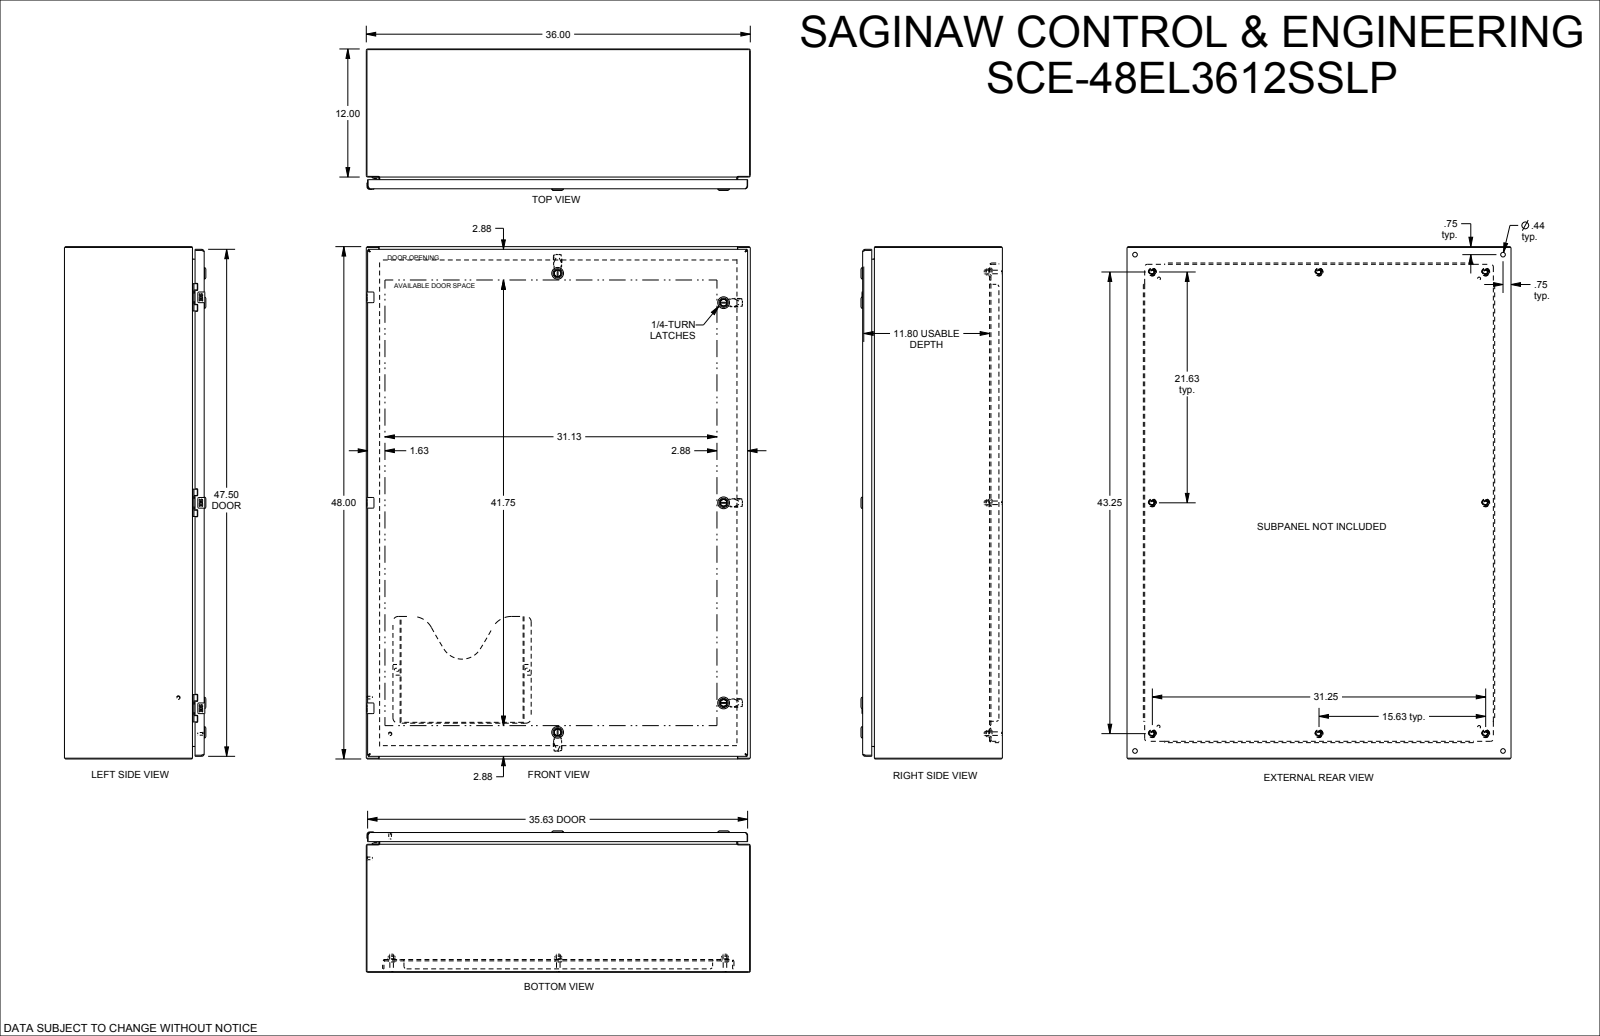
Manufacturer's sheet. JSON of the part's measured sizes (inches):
{"part_name": "SCE-48EL3612SSLP", "step_written_by": "SolidWorks 2019 (CONFIG_CONTROL_DESIGN)", "units": "inches", "bodies": {"solids": 0, "faces": 4985, "planar": 2437, "cylindrical": 1389, "other": 1159}, "overall_size": [48, 36, 13.256], "round_holes": [[0.394, 15], [0.367, 8], [0.5, 8], [0.172, 6], [0.205, 6], [0.244, 6], [0.266, 6], [0.197, 5], [0.315, 5], [0.634, 5], [0.281, 4], [0.375, 4]], "round_bosses_or_shafts": [[0.17, 9], [0.366, 8], [0.332, 8], [0.25, 6], [1.102, 5], [0.866, 5], [0.802, 5], [0.78, 5]], "partial_cylinders_radius": [[0.012, 142], [0.01, 52], [0.02, 52], [0.015, 36], [0.04, 23], [0.157, 20], [0.07, 14], [0.03, 13]], "face_to_face_distances": [0.075, 1, 0.104, 12.92, 12.995, 13.099, 13.024, 1.125, 11.795, 11.92], "hole_center_spacings": [2.461, 19.25, 1.274, 3.48, 4.262, 4.754, 38.5, 2.46]}
